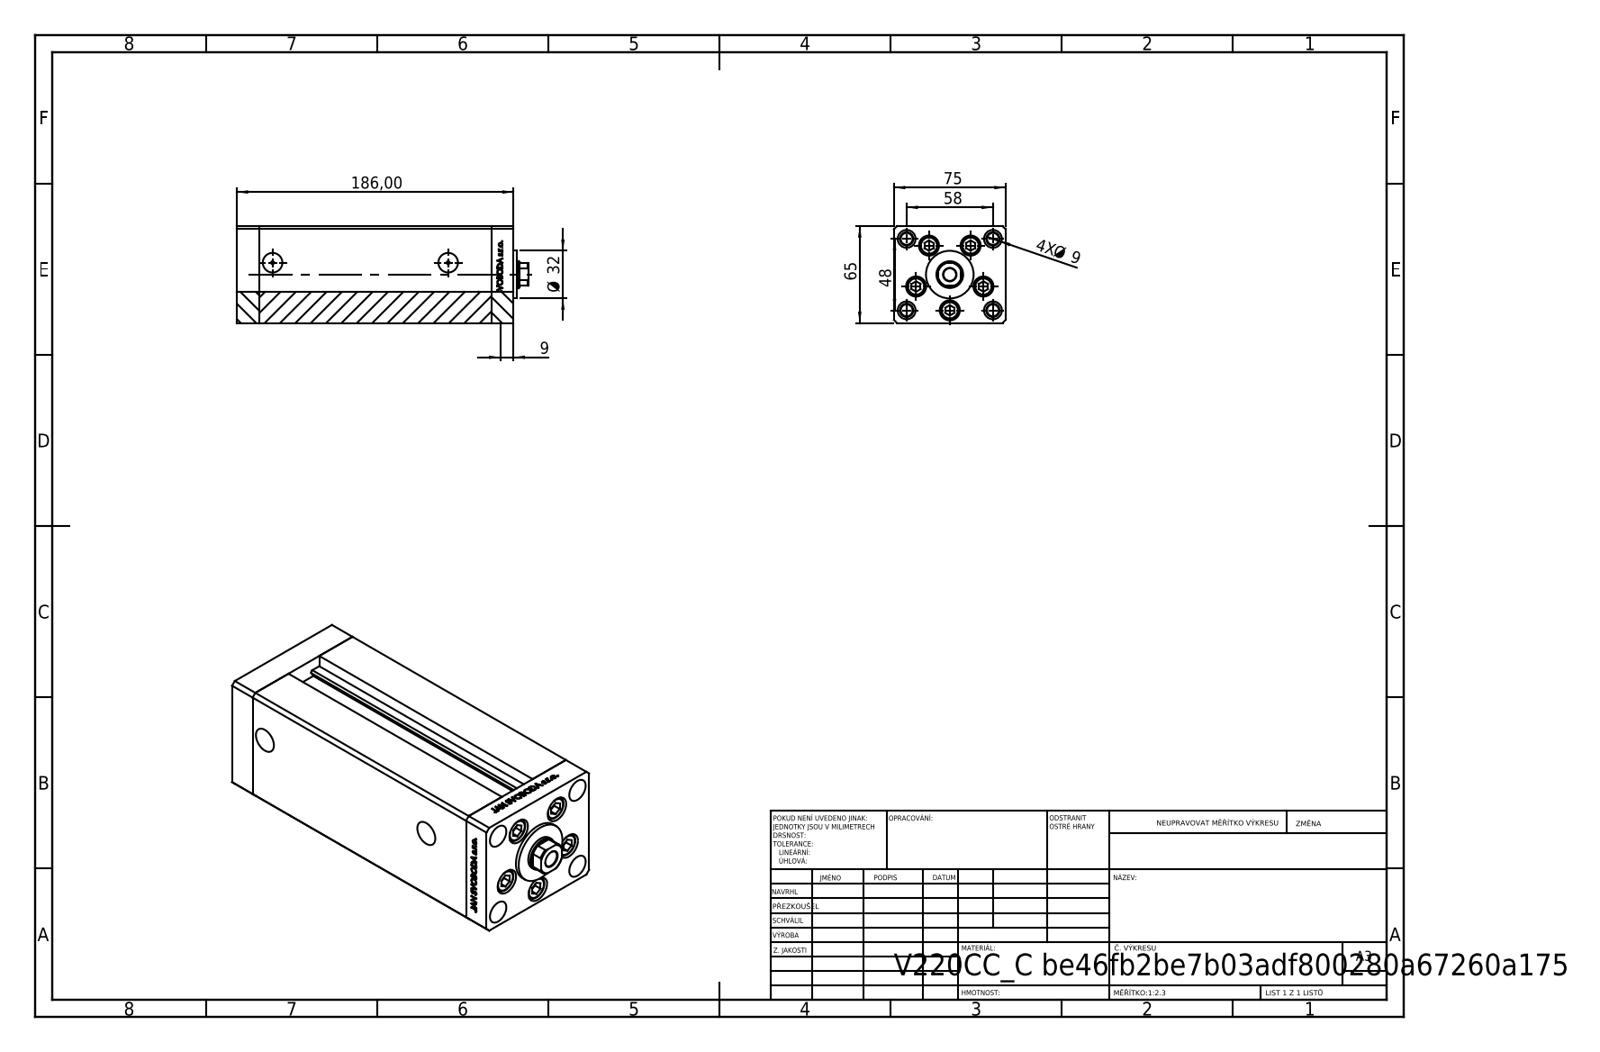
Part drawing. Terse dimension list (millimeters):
name: V220C_C MIDDLE; ALLEN BOLT; V220C BACK_C; V220C_VC_C (+1 more)
written by: SolidWorks 2019 (CONFIG_CONTROL_DESIGN)
unit: mm
bodies: 13 solids, 1169 faces (540 planar, 167 cylindrical, 462 other)
size: 196 × 75 × 65
volume: 757 889 mm³; area: 153 912 mm²
holes: 9× ⌀9, 5× ⌀13.5, 4× ⌀8, 4× ⌀12, 2× ⌀2, 2× ⌀13.16, 1× ⌀8.5, 1× ⌀12.5, 1× ⌀18
bosses: 5× ⌀8, 4× ⌀12.5, 1× ⌀32
rounds: 2× R0.93, 1× R8.5
face distances: 75, 65, 15, 156, 171, 186, 28, 54.5, 10.5, 26.25
hole spacings: 24, 37.64, 15.67, 17.22, 27.71, 28.83, 29, 32.63
